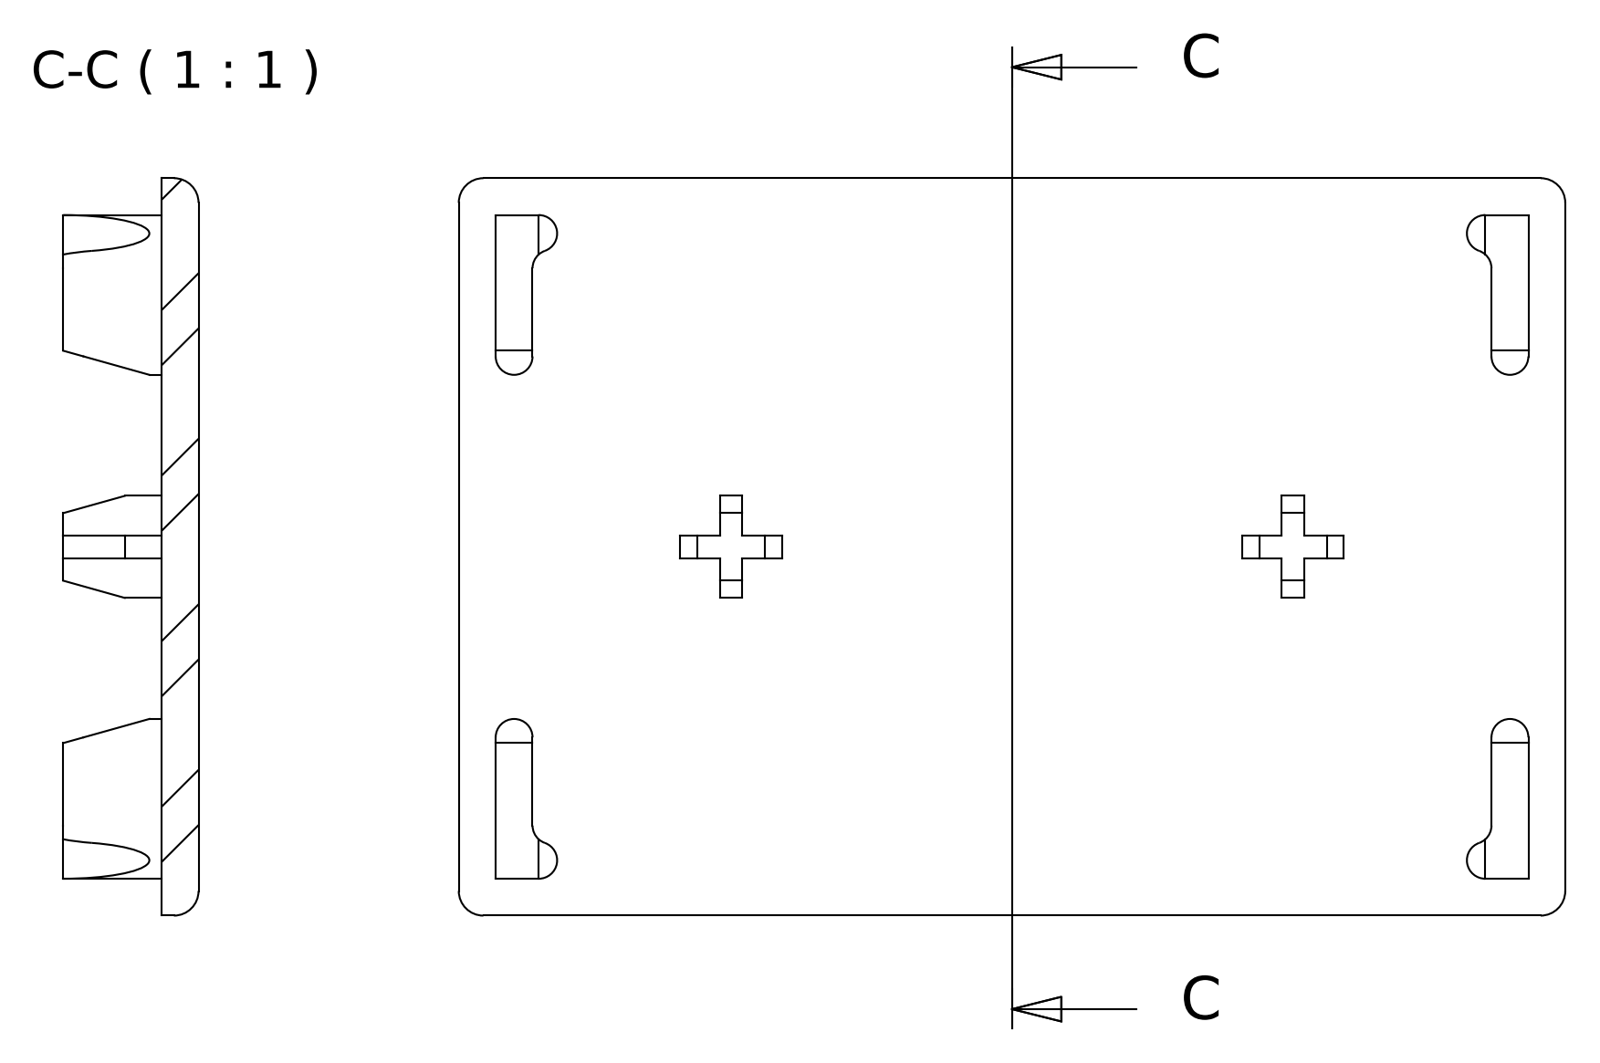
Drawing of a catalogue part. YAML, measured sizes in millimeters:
part_name: "DTPTR0000068"
step_written_by: "Autodesk Inventor 2016 (AUTOMOTIVE_DESIGN)"
units: millimeters
bodies: {solids: 1, faces: 88, planar: 64, cylindrical: 20, other: 4}
overall_size: [90, 60, 11]
volume: 17600
surface_area: 12863
partial_cylinders:
  - {radius: 1.5, count: 12}
  - {radius: 2, count: 8}
face_to_face_distances: [3, 84, 81, 1.8, 8, 11, 29.1, 30.9, 78, 6]
